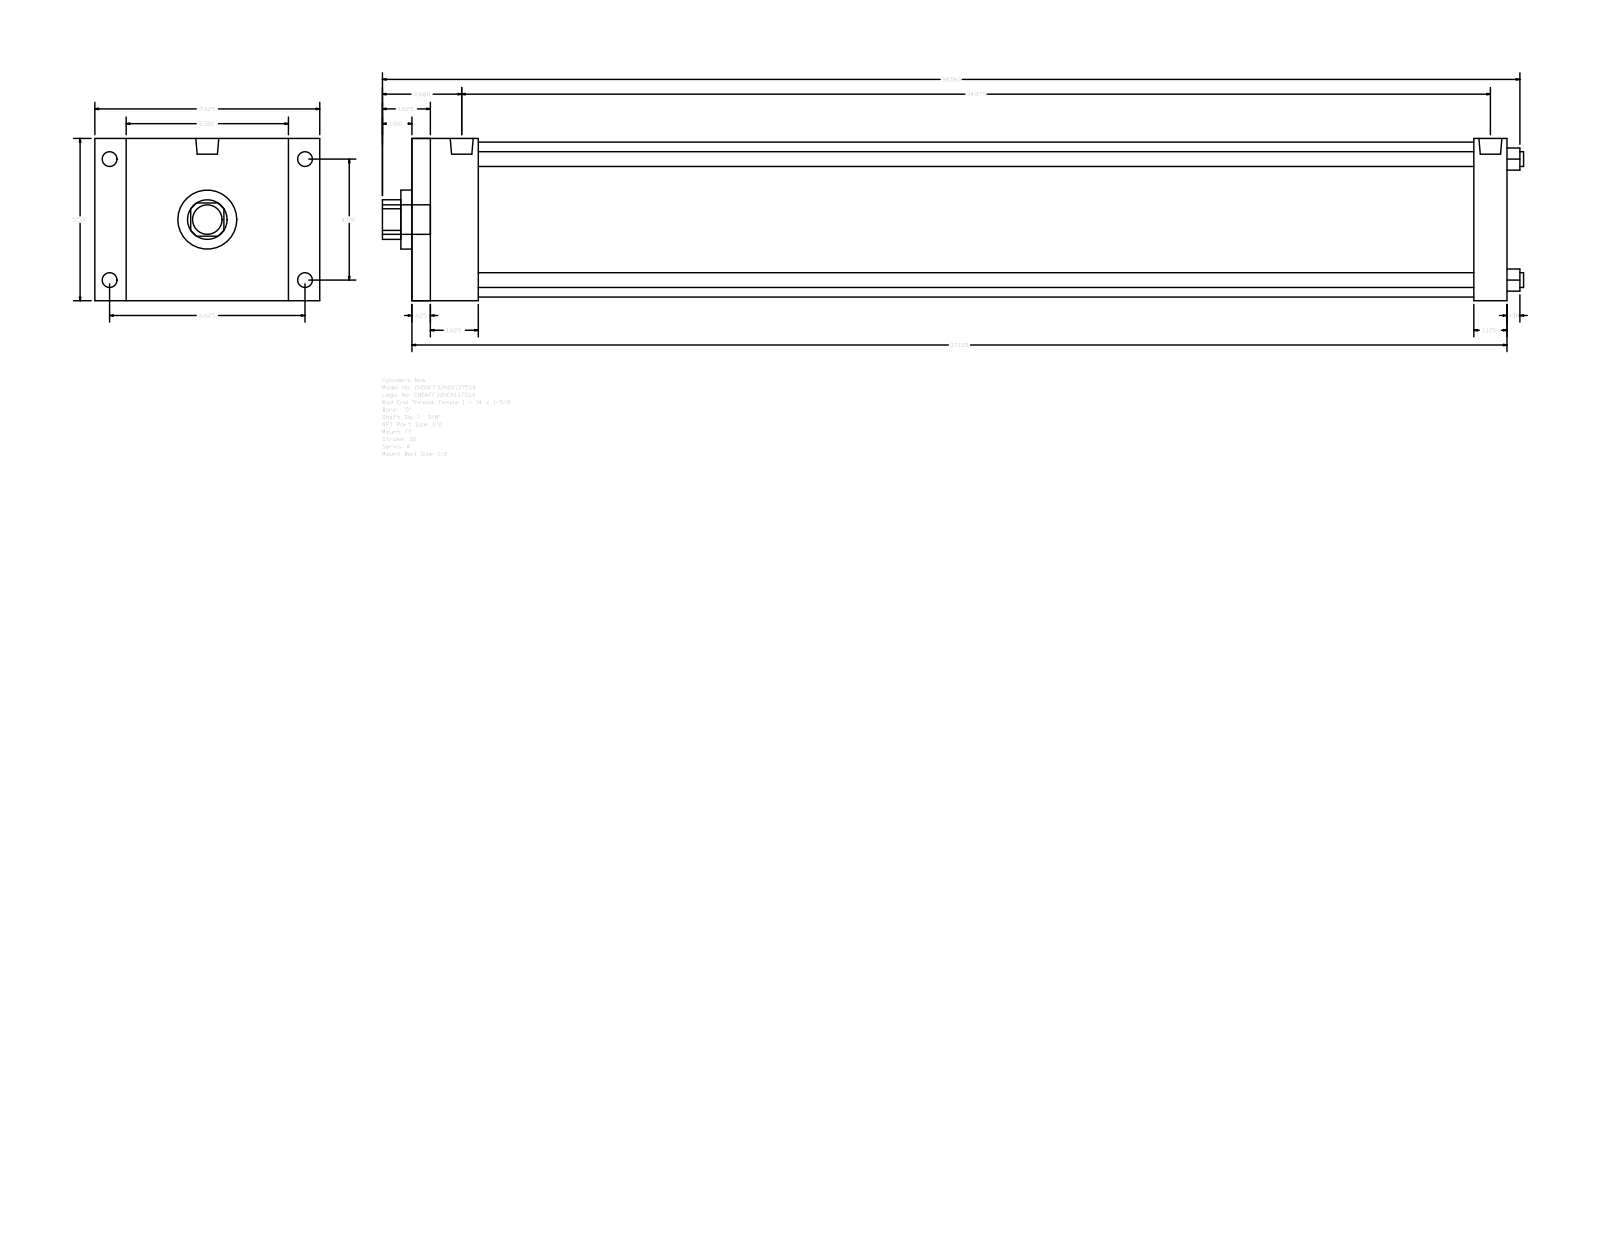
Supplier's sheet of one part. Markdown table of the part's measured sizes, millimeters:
| quantity | value |
| --- | --- |
| part name | A_FF__0500_1.375 |
| STEP written by | GSSL Pune (CONFIG_CONTROL_DESIGN) |
| units | millimeters |
| bodies | 0 solids, 92 faces (64 planar, 28 cylindrical, 0 other) |
| overall size | 982.66 × 193.68 × 139.7 |
| round holes (diameter × count) | 12.7 × 4, 34.92 × 1, 50.8 × 1, 133.35 × 1 |
| round bosses / shafts (diameter × count) | 12.7 × 4, 8.73 × 4, 19.77 × 2, 25.4 × 1 |
| partial cylindrical surfaces (radius × count) | 17.06 × 1 |
| main face-to-face distances | 139.7, 942.98, 15.87, 927.11, 28.58, 914.4, 898.53, 57.15, 41.28, 857.25 |
| hole center spacings | 73.64, 104.14, 147.28 |
